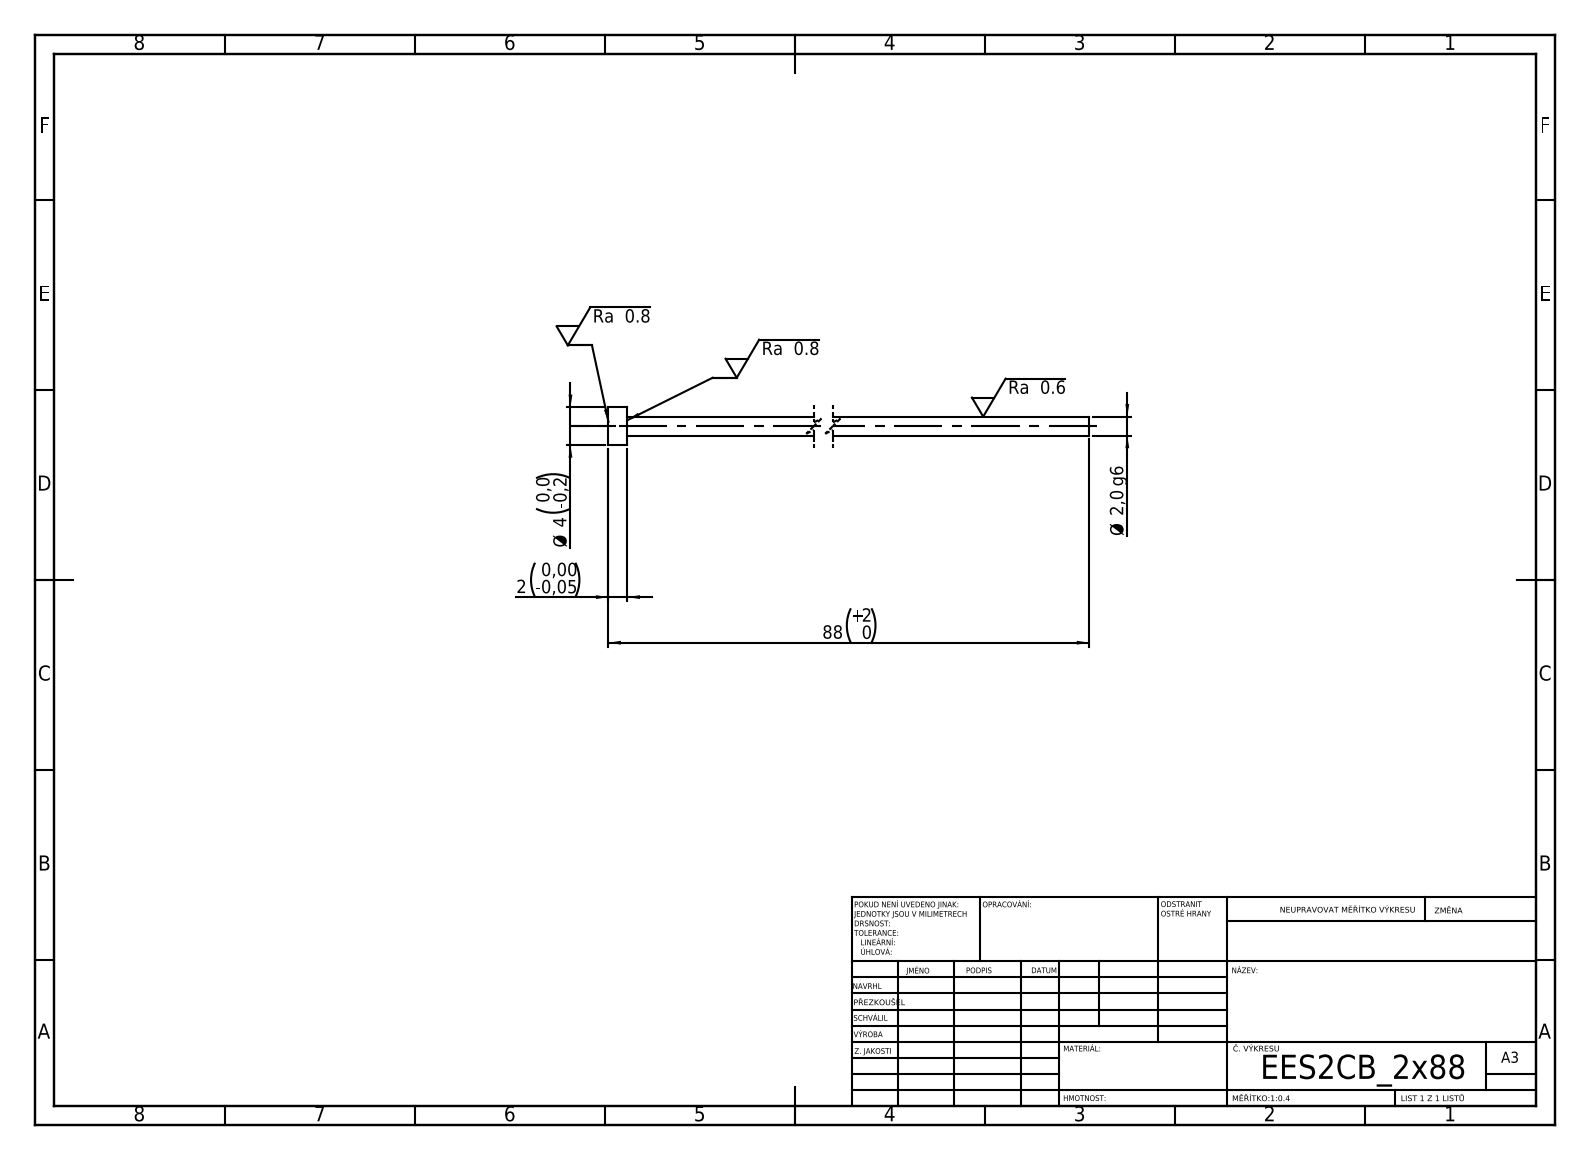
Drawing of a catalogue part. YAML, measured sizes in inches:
step_written_by: "SolidWorks 2019 (CONFIG_CONTROL_DESIGN)"
units: inches
bodies: {solids: 1, faces: 7, planar: 3, cylindrical: 4, other: 0}
overall_size: [3.465, 0.157, 0.157]
volume: 0.018
surface_area: 0.916
round_bosses_or_shafts:
  - {diameter: 0.157, count: 1}
  - {diameter: 0.079, count: 1}
face_to_face_distances: [0.079, 3.465, 3.386]
